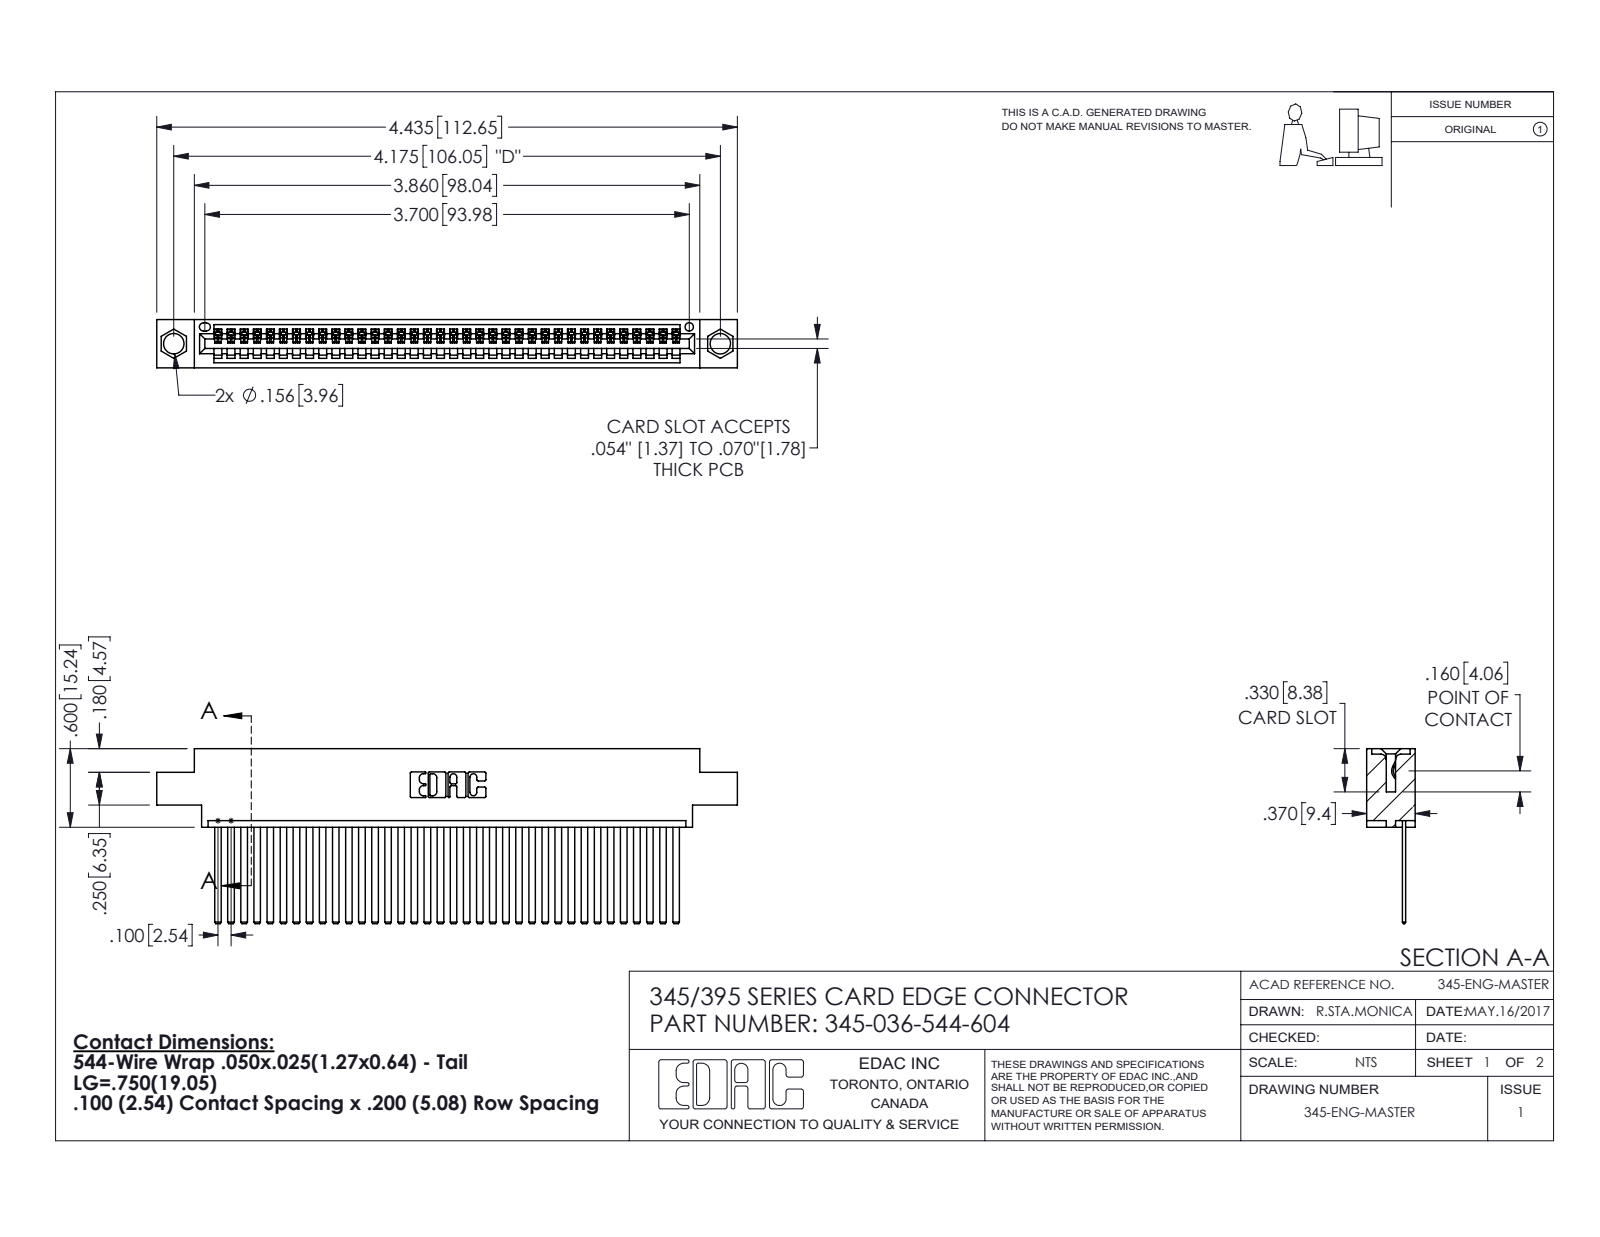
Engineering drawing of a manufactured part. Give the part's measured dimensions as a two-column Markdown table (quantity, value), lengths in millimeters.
| quantity | value |
| --- | --- |
| part name | 345 Part_0.170 Offset - 0.156 Dia-TH; 345-292-001_345-293-144; 345-036-544-604 |
| STEP written by | SolidWorks 2016 (CONFIG_CONTROL_DESIGN) |
| units | millimeters |
| bodies | 37 solids, 2002 faces (1380 planar, 622 cylindrical, 0 other) |
| overall size | 112.6 × 34 × 9.4 |
| volume | 10 900 mm³ |
| surface area | 15 550 mm² |
| round holes (diameter × count) | 4 × 2, 1.6 × 1 |
| partial cylindrical surfaces (radius × count) | 0.2 × 72, 0.3 × 22, 0.2 × 6, 0.8 × 6, 0.7 × 3, 0.8 × 2, 1 × 2, 0.4 × 1 |
| main face-to-face distances | 1.8, 7.6, 0.6, 2.5, 6.9, 9.4, 5.1, 5.7, 4.4, 3.8 |
| hole center spacings | 6.9, 100.1, 106 |
